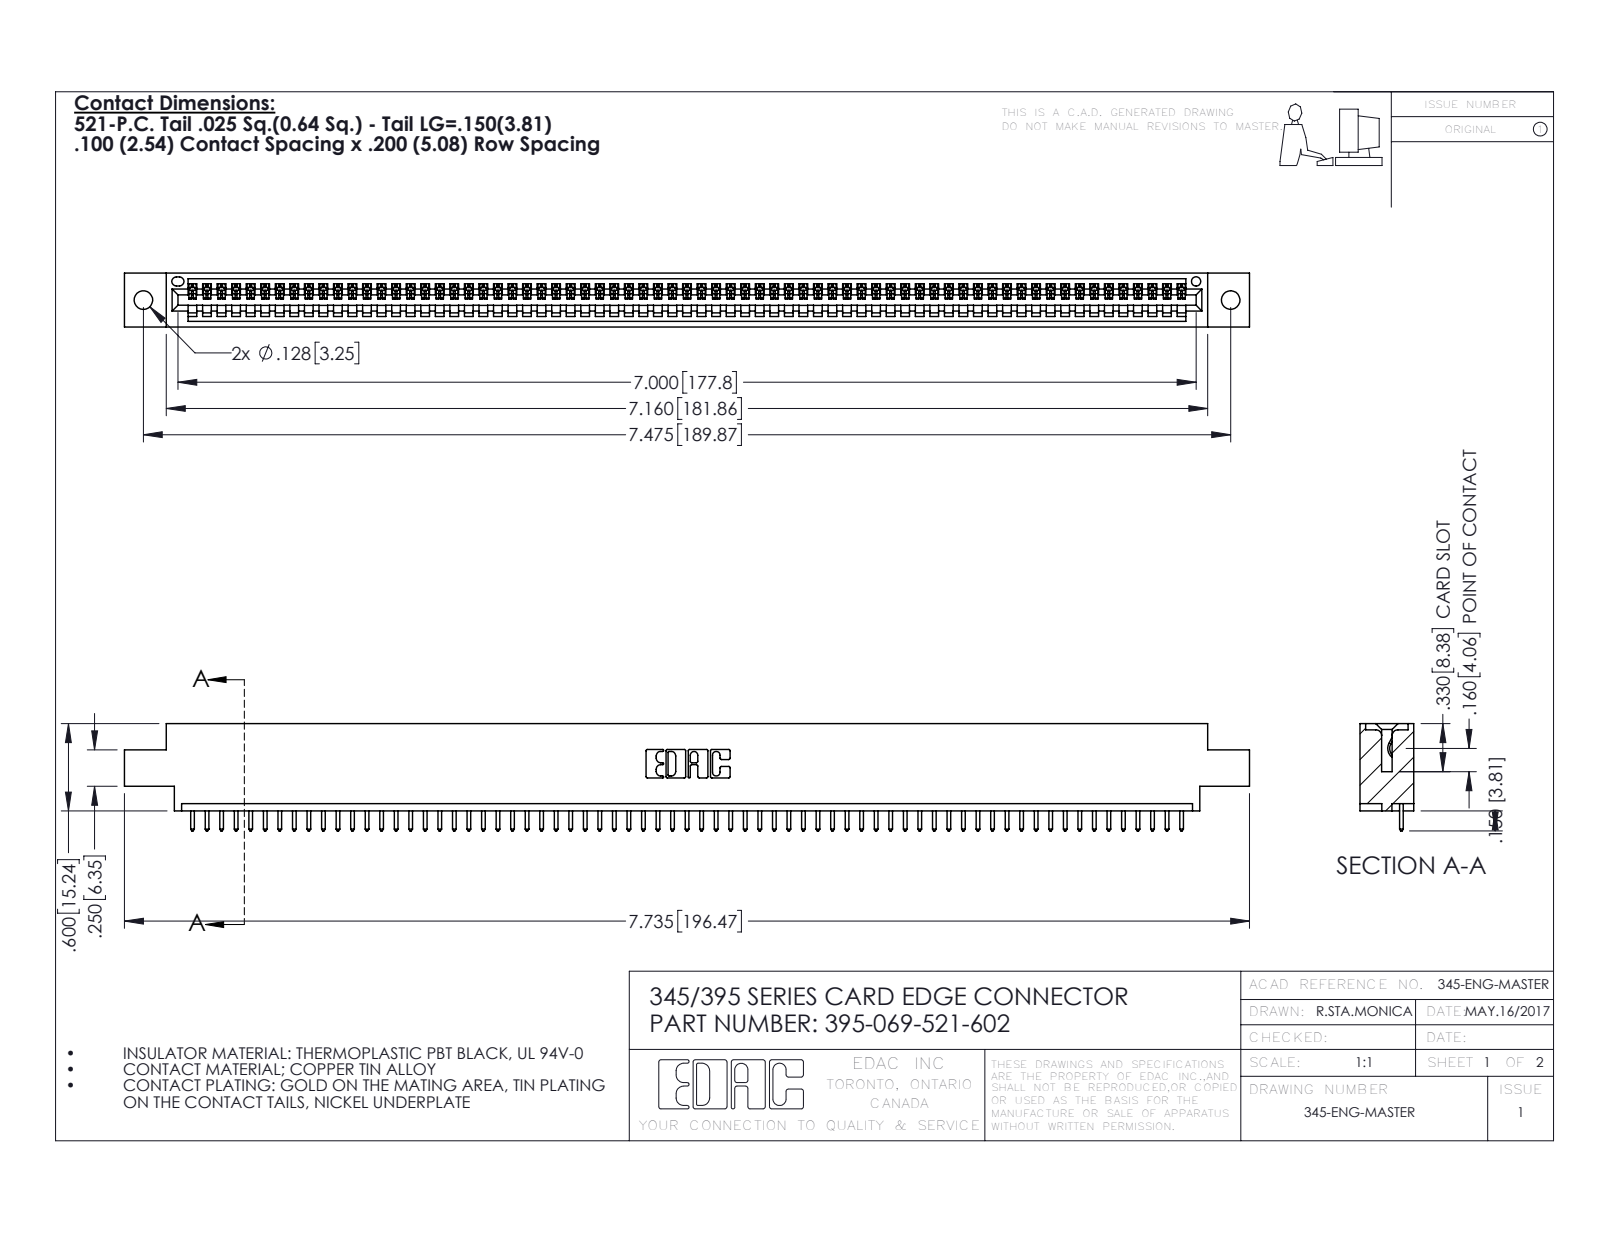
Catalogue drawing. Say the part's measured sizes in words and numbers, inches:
The part is named "395-069-521-602; 345 Part_0.170 Offset - 0.128 Dia; 345-292-001_345-293-121". Its 3-D file was written by "SolidWorks 2016 (CONFIG_CONTROL_DESIGN)". It is 70 solids with 4132 faces: 2844 planar, 1288 cylindrical and 0 other. Overall it measures 7.735 by 0.737 by 0.37 inches. Its volume is 1.131 cubic inches and its surface area 37.33 square inches. Round holes: 2 of diameter 0.128, 1 of diameter 0.064. Partial cylindrical surfaces (rounded edges, fillets, slot ends): 138 of radius 0.006, 138 of radius 0.01, 22 of radius 0.01, 6 of radius 0.007, 6 of radius 0.031, 3 of radius 0.026, 2 of radius 0.031, 2 of radius 0.04. The main face-to-face distances are 0.072, 0.298, 0.37, 0.2, 0.098, 0.272, 0.025, 0.225, 0.175, 0.149. The hole center spacings are 0.27, 7.239, 7.475.
